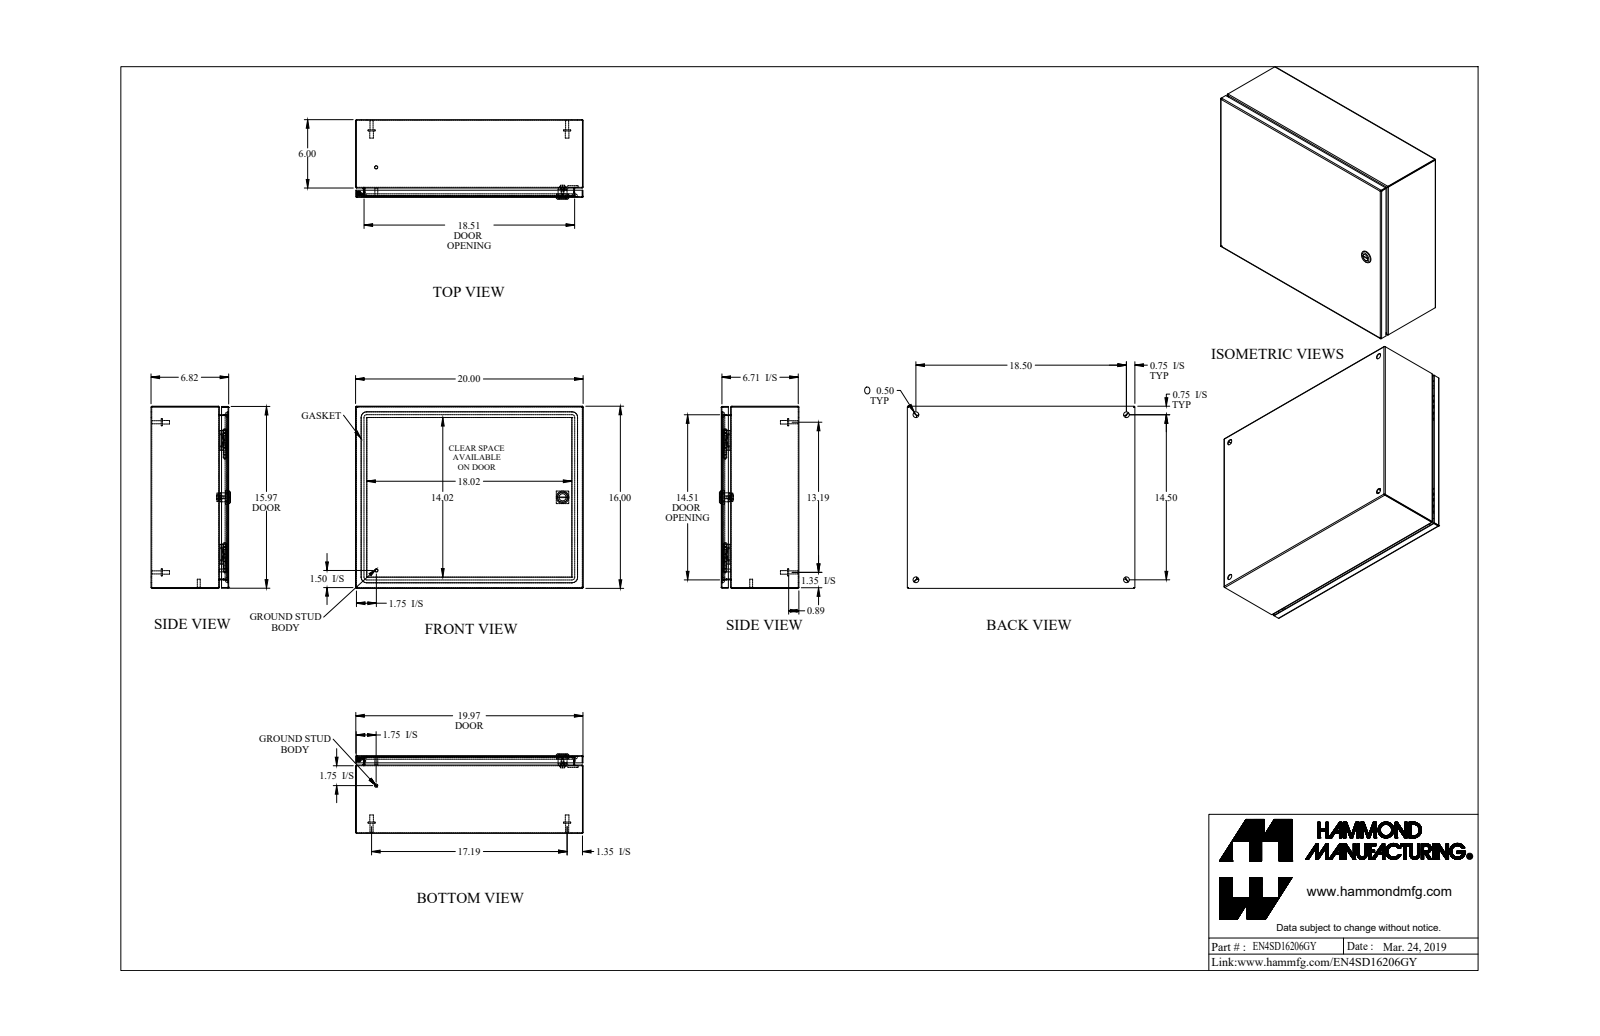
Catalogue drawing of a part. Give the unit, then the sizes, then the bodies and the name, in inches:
Units: inches
Overall size (bounding box): 20 × 16 × 6.982
Round holes (diameter × count): ⌀0.5 ×4, ⌀0.172 ×1, ⌀0.232 ×1, ⌀0.24 ×1, ⌀0.242 ×1, ⌀0.625 ×1, ⌀0.785 ×1
Round bosses / shafts (diameter × count): ⌀0.625 ×4, ⌀0.313 ×4, ⌀0.27 ×4, ⌀0.281 ×2, ⌀0.25 ×2, ⌀1.1 ×1, ⌀0.525 ×1, ⌀0.455 ×1
Partial cylindrical surfaces — rounded edges, fillets, slot ends (radius × count): R0.029 ×21, R0.086 ×21, R0.25 ×16, R19 ×8, R0.006 ×4, R0.062 ×4, R0.499 ×4, R0.125 ×2
Main face-to-face distances: 0.057, 6.765, 6.708, 6.822, 15.943, 19.943, 15.886, 16, 19.886, 20
Hole centre spacings: 14.5, 18.5, 18.888, 23.506, 7.326, 7.327
Volume: 76.29 in³ · Surface area: 2 585 in²
Bodies: 21 solids, 634 faces (285 planar, 213 cylindrical, 136 other)
Part name (STEP PRODUCT): EN4SD16206GY_Default
STEP written by: SolidWorks 2019 (CONFIG_CONTROL_DESIGN)
